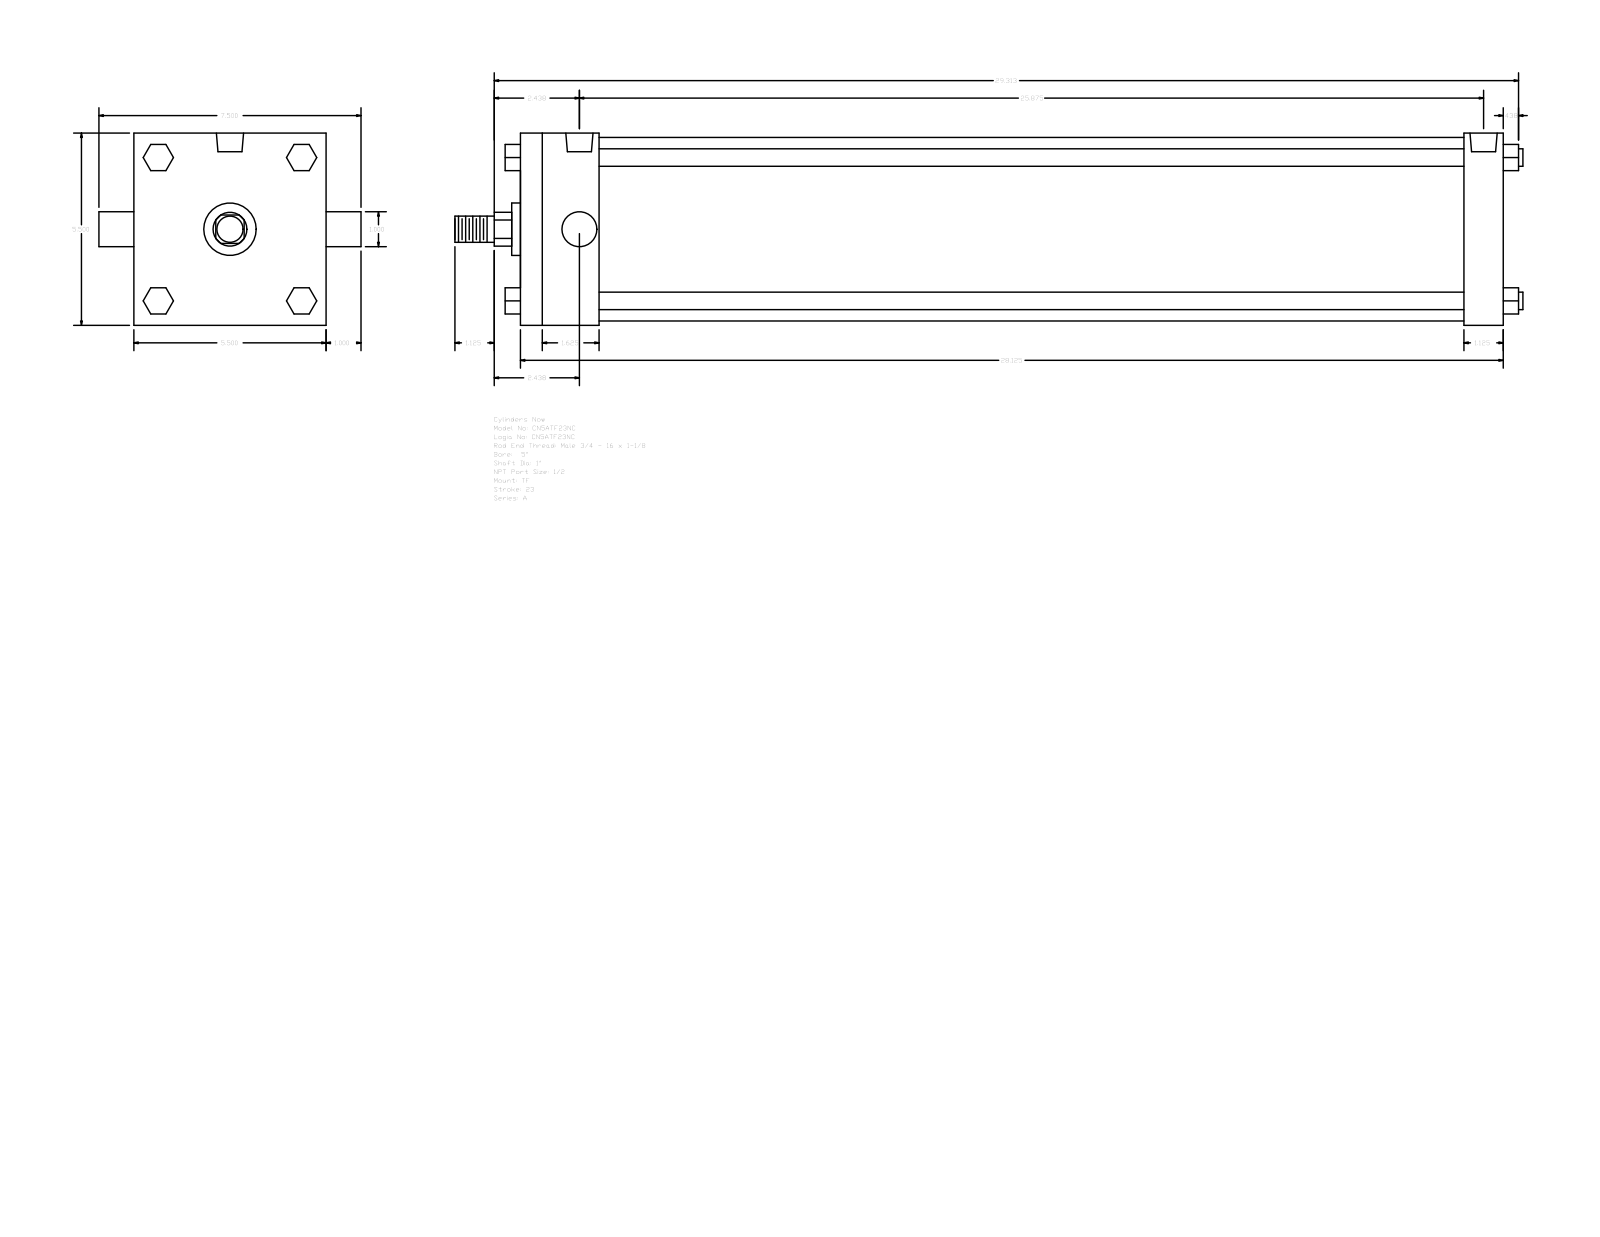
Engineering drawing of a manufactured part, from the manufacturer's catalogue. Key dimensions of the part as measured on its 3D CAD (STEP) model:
Part name (STEP PRODUCT): A_TF__0500_1
STEP written by: GSSL Pune (CONFIG_CONTROL_DESIGN)
Units: millimetres
Bodies: 0 solids, 120 faces (92 planar, 28 cylindrical, 0 other)
Overall size (bounding box): 776.29 × 190.5 × 139.7
Round holes (diameter × count): ⌀8.73 ×3, ⌀19.77 ×2
Round bosses / shafts (diameter × count): ⌀12.7 ×4, ⌀25.4 ×2, ⌀133.35 ×1, ⌀38.1 ×1, ⌀19.05 ×1
Partial cylindrical surfaces — rounded edges, fillets, slot ends (radius × count): R12.29 ×1
Main face-to-face distances: 139.7, 714.37, 28.57, 685.8, 57.15, 628.65, 657.22, 19.05, 52.07, 90.18
Hole centre spacings: 2.39, 654.84, 652.45, 657.23
